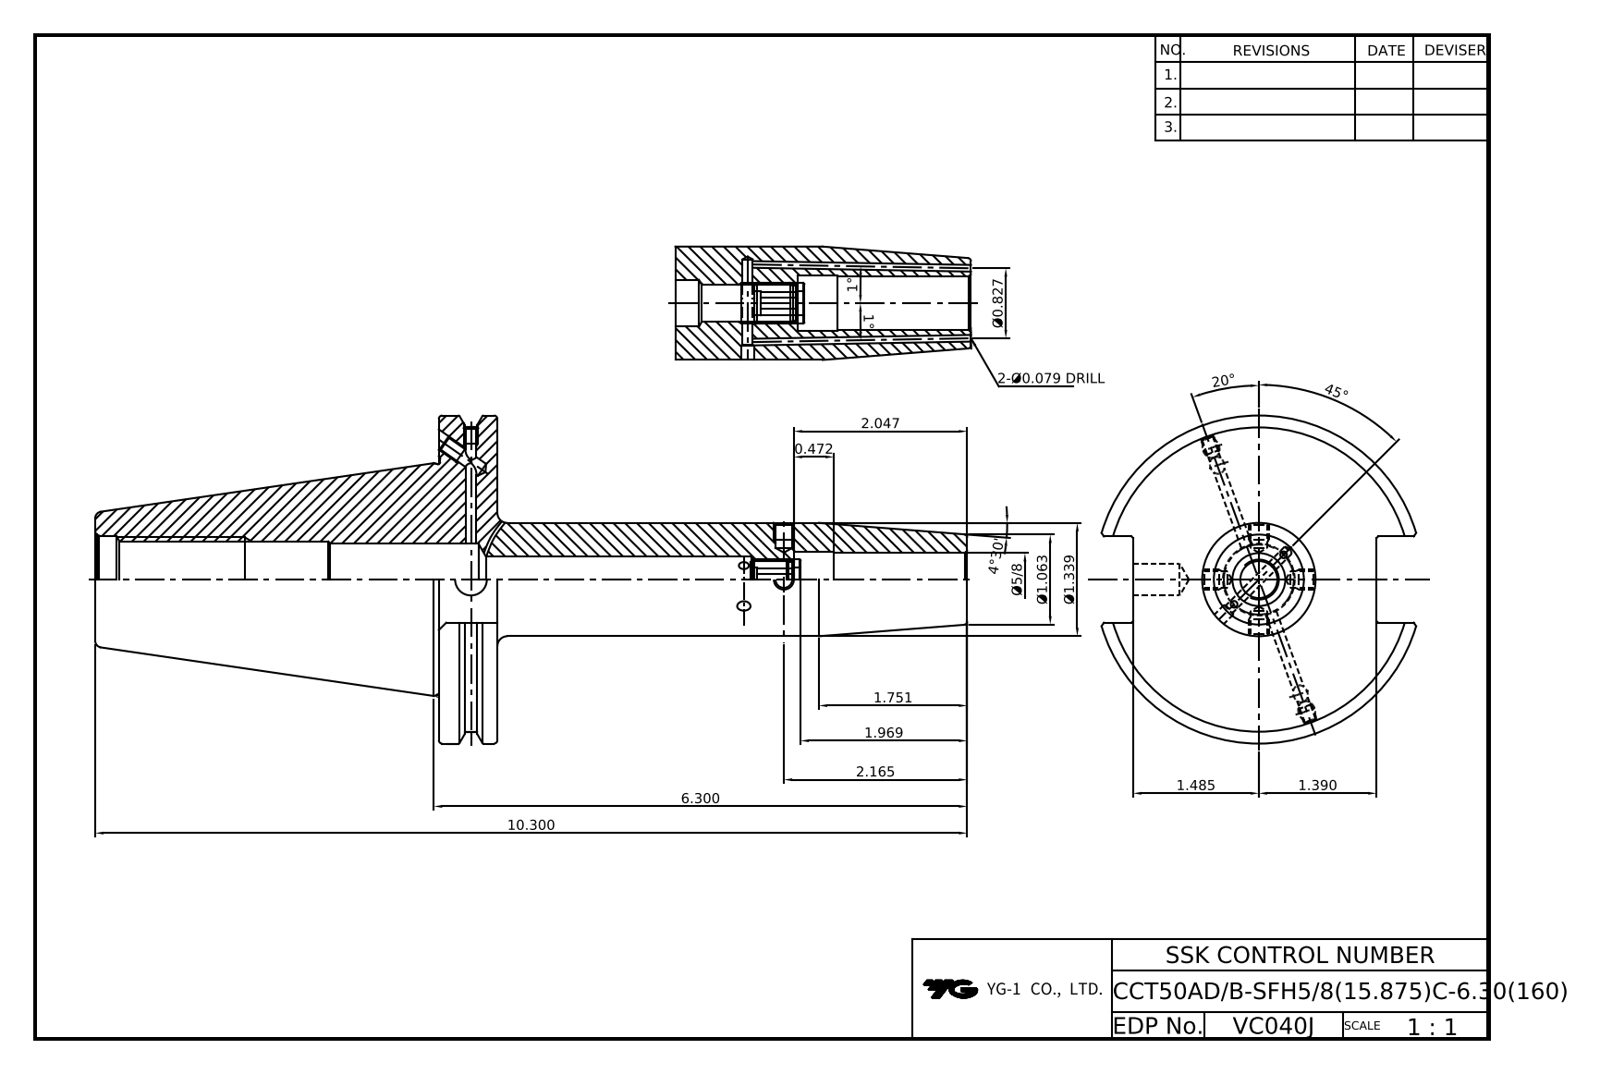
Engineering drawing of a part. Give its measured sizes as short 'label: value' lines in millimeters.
name: LO-CCT50ADB-SFH15.875C-6.30(20240115)
written by: Autodesk Inventor 2024 (AUTOMOTIVE_DESIGN)
unit: mm
bodies: 1 solid, 94 faces (38 planar, 30 cylindrical, 26 other)
size: 261.6 × 98.42 × 94.69
volume: 421 185 mm³; area: 66 521 mm²
holes: 2× ⌀2.5, 2× ⌀3.24, 2× ⌀4.13, 2× ⌀4.2, 2× ⌀5, 1× ⌀9.53, 1× ⌀10.92, 1× ⌀14, 1× ⌀15.88, 1× ⌀17.08, 1× ⌀21.5, 1× ⌀21.97
bosses: 1× ⌀98.42, 1× ⌀91.29, 1× ⌀69.25, 1× ⌀34
face distances: 17.55, 103.1, 120.65, 73.03, 25.9, 261.6, 158.5, 140.95, 103.5, 0.4
